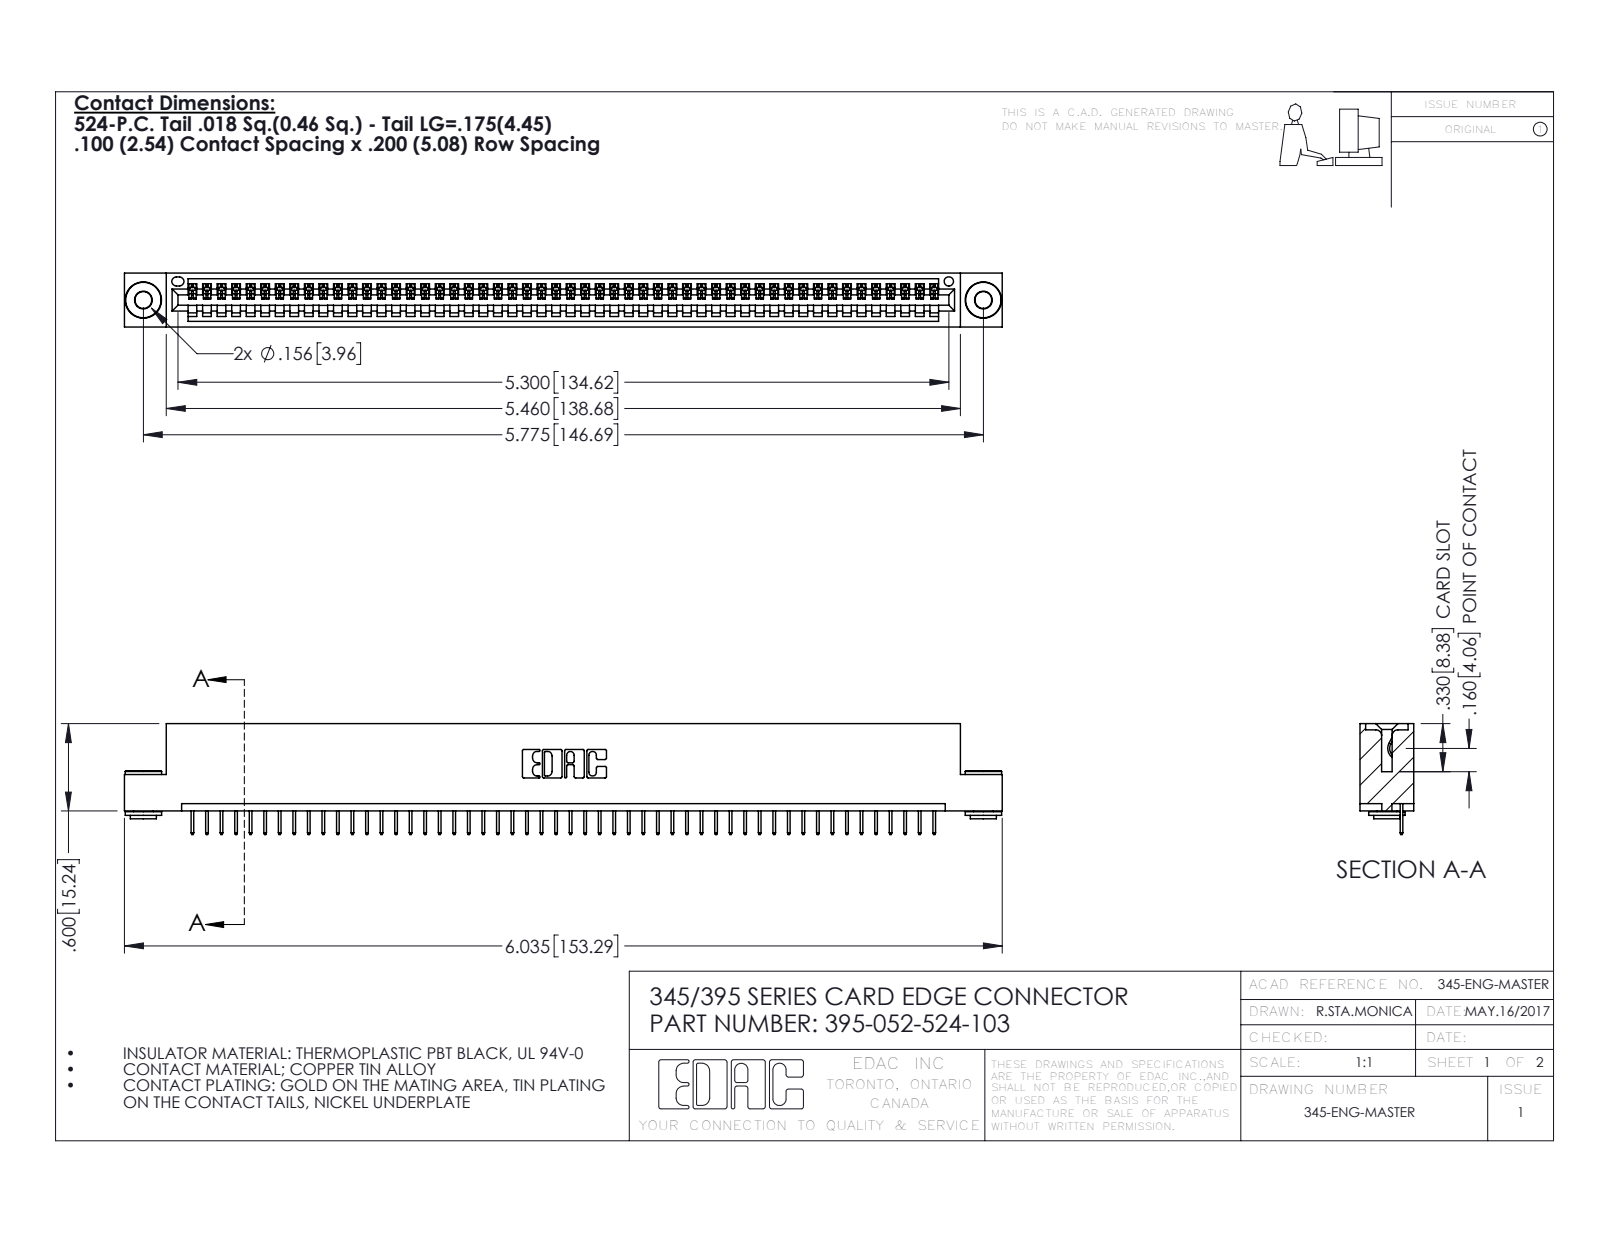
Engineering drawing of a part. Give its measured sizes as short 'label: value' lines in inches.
name: 395-052-524-103; 345-292-001_345-293-124; 345-250-002_345-250-002-102; 345 Part_Flush Mounting Lugs - 0.156 Dia-TH
written by: SolidWorks 2016 (CONFIG_CONTROL_DESIGN)
unit: in
bodies: 55 solids, 3388 faces (2482 planar, 898 cylindrical, 8 other)
size: 6.035 × 0.762 × 0.37
volume: 0.882 in³; area: 29.3 in²
holes: 2× ⌀0.116, 2× ⌀0.156, 1× ⌀0.064
bosses: 2× ⌀0.25, 2× ⌀0.18, 2× ⌀0.136
rounds: 104× R0.006, 22× R0.01, 6× R0.007, 6× R0.031, 3× R0.026, 2× R0.031, 2× R0.04, 1× R0.014
face distances: 0.072, 0.298, 0.37, 0.2, 0.025, 0.098, 0.272, 0.225, 0.072, 0.149
hole spacings: 0.27, 5.539, 5.775
